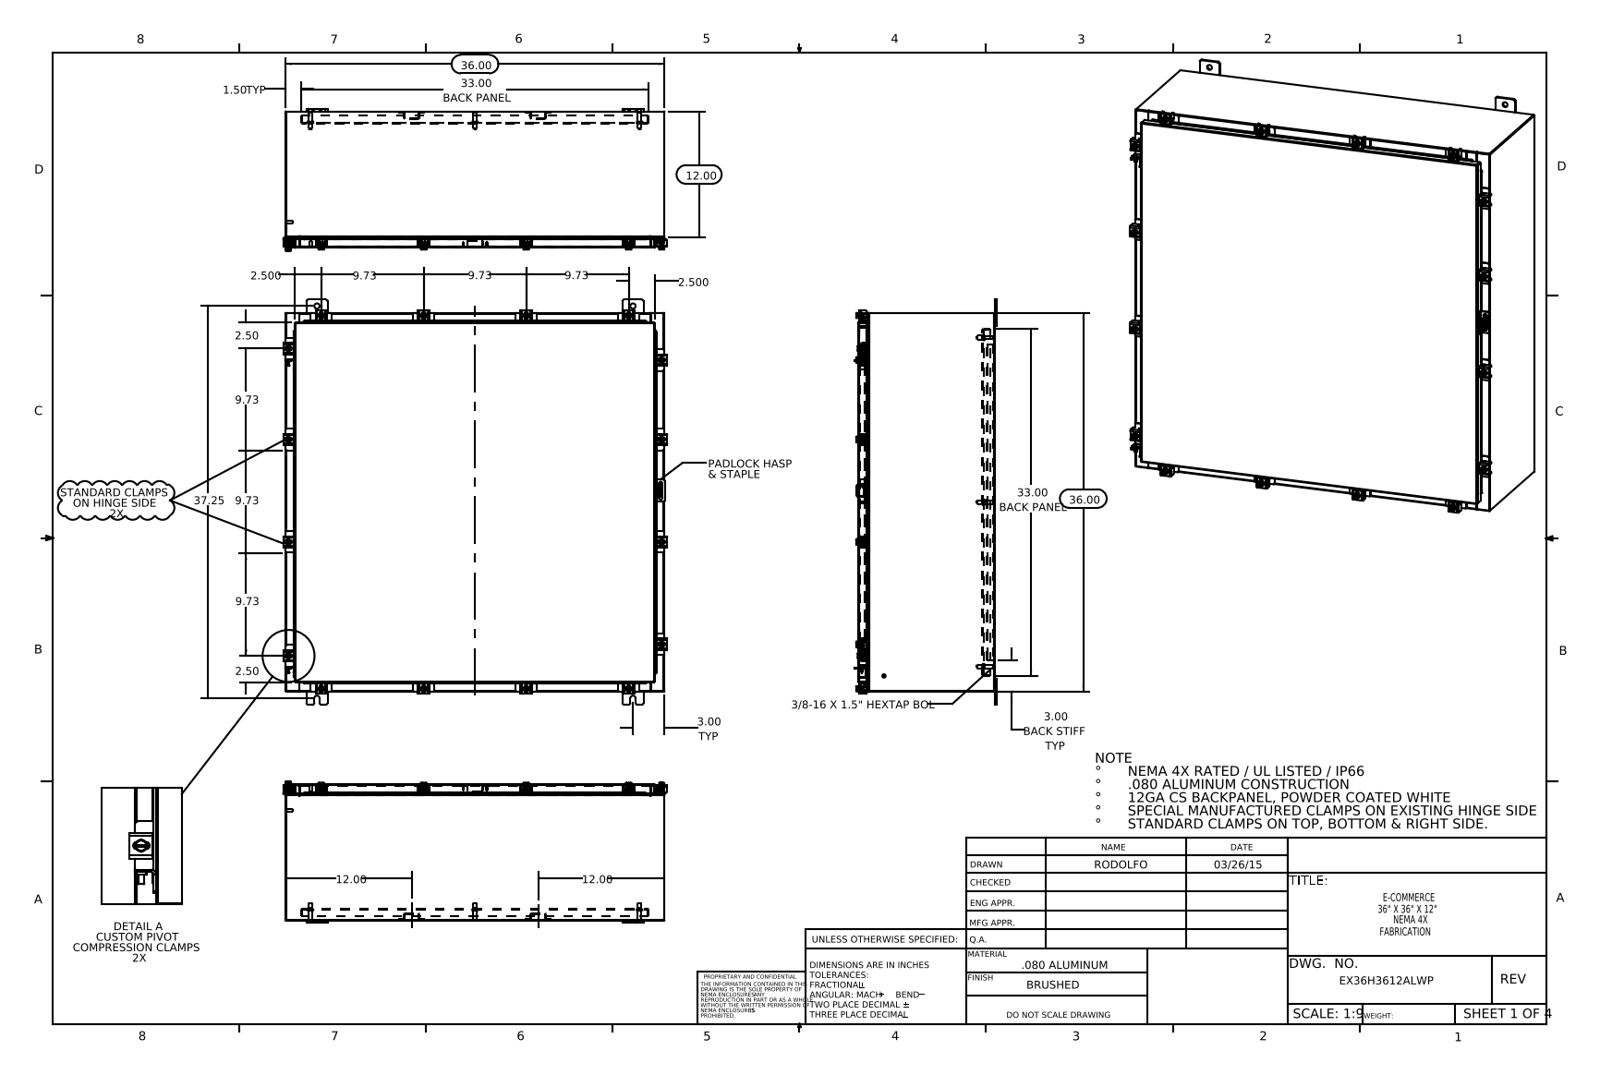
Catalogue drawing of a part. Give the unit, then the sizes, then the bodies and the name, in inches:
Units: inches
Overall size (bounding box): 38.5 × 36.421 × 13.453
Round holes (diameter × count): ⌀0.213 ×16, ⌀0.26 ×16, ⌀0.5 ×12, ⌀0.25 ×7, ⌀0.125 ×1
Round bosses / shafts (diameter × count): ⌀0.5 ×16, ⌀0.25 ×16, ⌀0.399 ×14, ⌀0.625 ×8, ⌀0.375 ×8, ⌀0.33 ×8, ⌀0.157 ×6, ⌀0.14 ×6
Partial cylindrical surfaces — rounded edges, fillets, slot ends (radius × count): R0.06 ×70, R0.013 ×38, R0.088 ×34, R0.141 ×32, R0.12 ×30, R0.19 ×24, R0.09 ×22, R0.05 ×21
Main face-to-face distances: 0.075, 12.9, 35.925, 12.826, 12.975, 0.104, 1, 1.075, 11.826, 11.9
Hole centre spacings: 2.34, 14.744, 15.625, 17.756, 1.969, 5.288, 5.299, 7.043
Volume: 504.6 in³ · Surface area: 12 594 in²
Bodies: 114 solids, 2822 faces (1459 planar, 1083 cylindrical, 280 other)
Part name (STEP PRODUCT): EX36H3612ALWP Enclosure Stiffener; HW-CLN-NH-20330; EX36H3612ALWP Mounting Studs; EX36H3612ALWP Clamp Bracket (+8 more)
STEP written by: SolidWorks 2014 (CONFIG_CONTROL_DESIGN)
